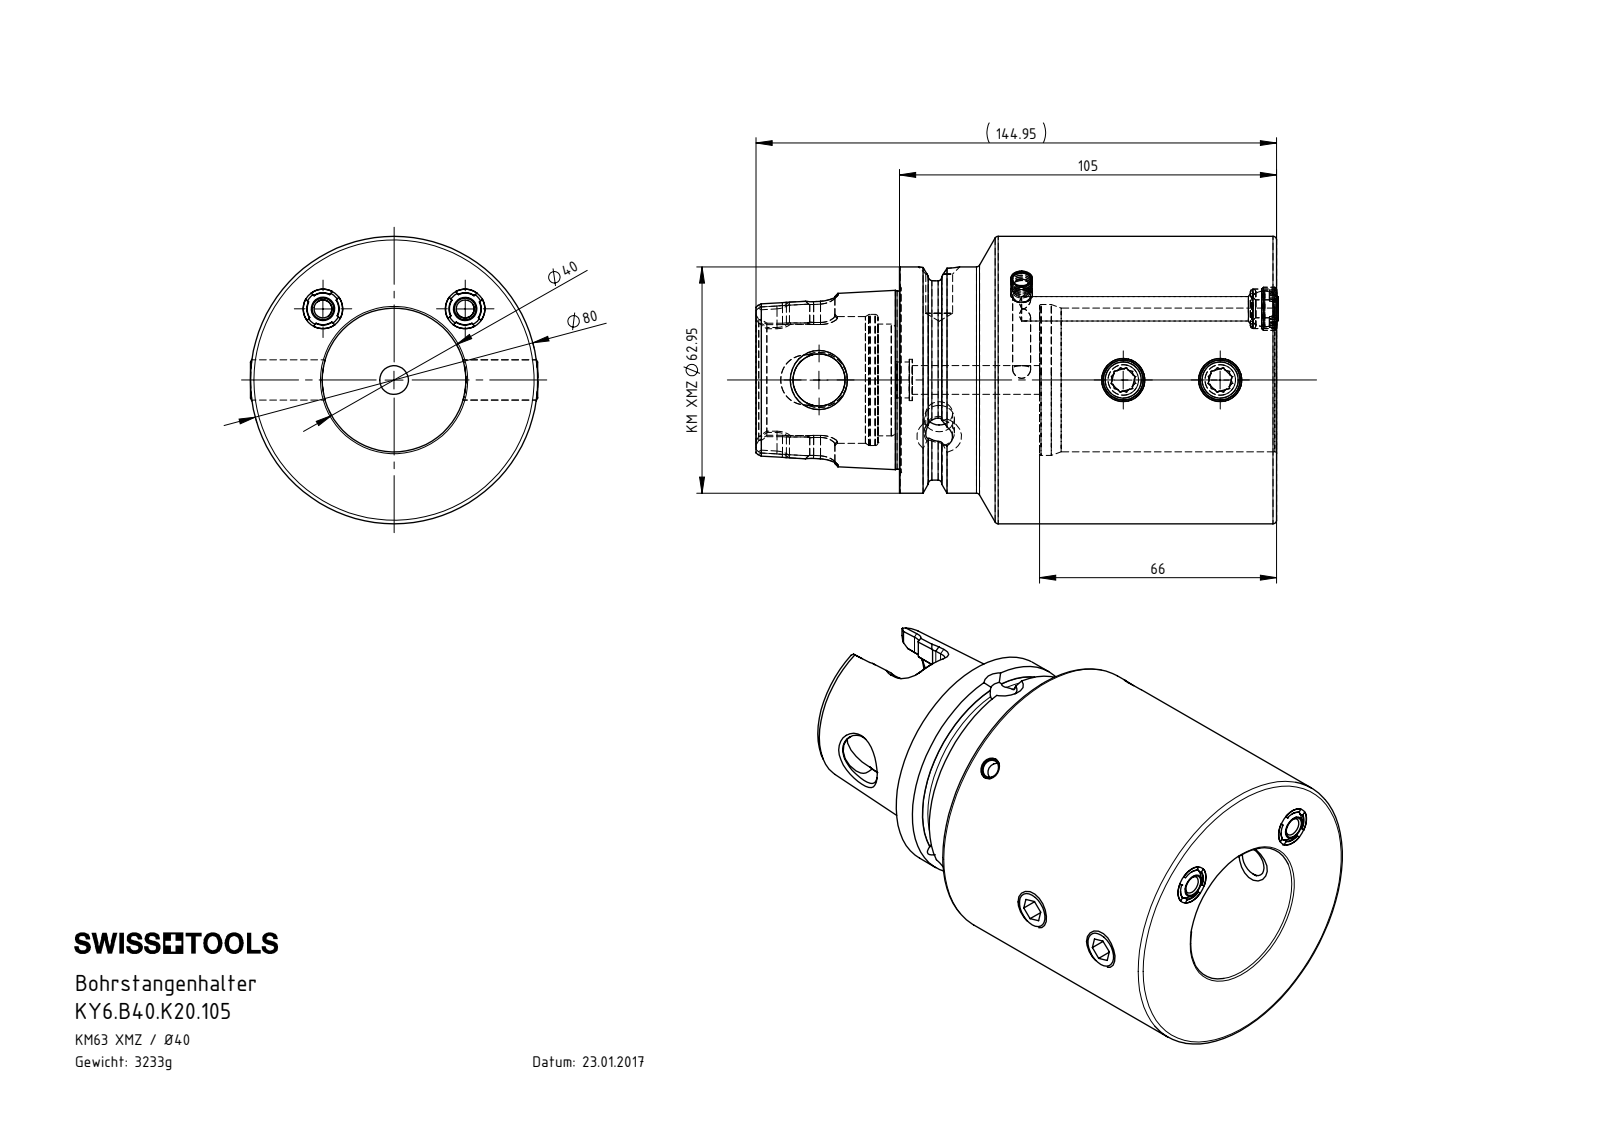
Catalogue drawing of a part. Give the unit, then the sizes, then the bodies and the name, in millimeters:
Units: millimetres
Overall size (bounding box): 145.91 × 80 × 80
Round holes (diameter × count): ⌀10 ×3, ⌀5 ×2, ⌀6 ×2, ⌀6.8 ×2, ⌀7.47 ×2, ⌀11 ×2, ⌀11.2 ×2, ⌀8 ×1, ⌀8.48 ×1, ⌀11.5 ×1, ⌀14.5 ×1, ⌀31.1 ×1
Round bosses / shafts (diameter × count): ⌀12 ×4, ⌀80 ×1, ⌀62.95 ×1, ⌀55.7 ×1
Partial cylindrical surfaces — rounded edges, fillets, slot ends (radius × count): R4 ×6, R4.4 ×2, R7.04 ×2
Main face-to-face distances: 66, 39, 105, 1.1, 40.1, 106.1, 6, 12, 4.9, 45
Hole centre spacings: 30, 27, 42.42, 84.7, 111.7
Volume: 419 113 mm³ · Surface area: 65 722 mm²
Bodies: 9 solids, 384 faces (119 planar, 102 cylindrical, 163 other)
Part name (STEP PRODUCT): KY6-B40.K20.105; KU1-U12.002.010; KU1-U12.002.010_A; KU1-U12.003.010_A (+2 more)
STEP written by: SolidWorks 2012 (CONFIG_CONTROL_DESIGN)
